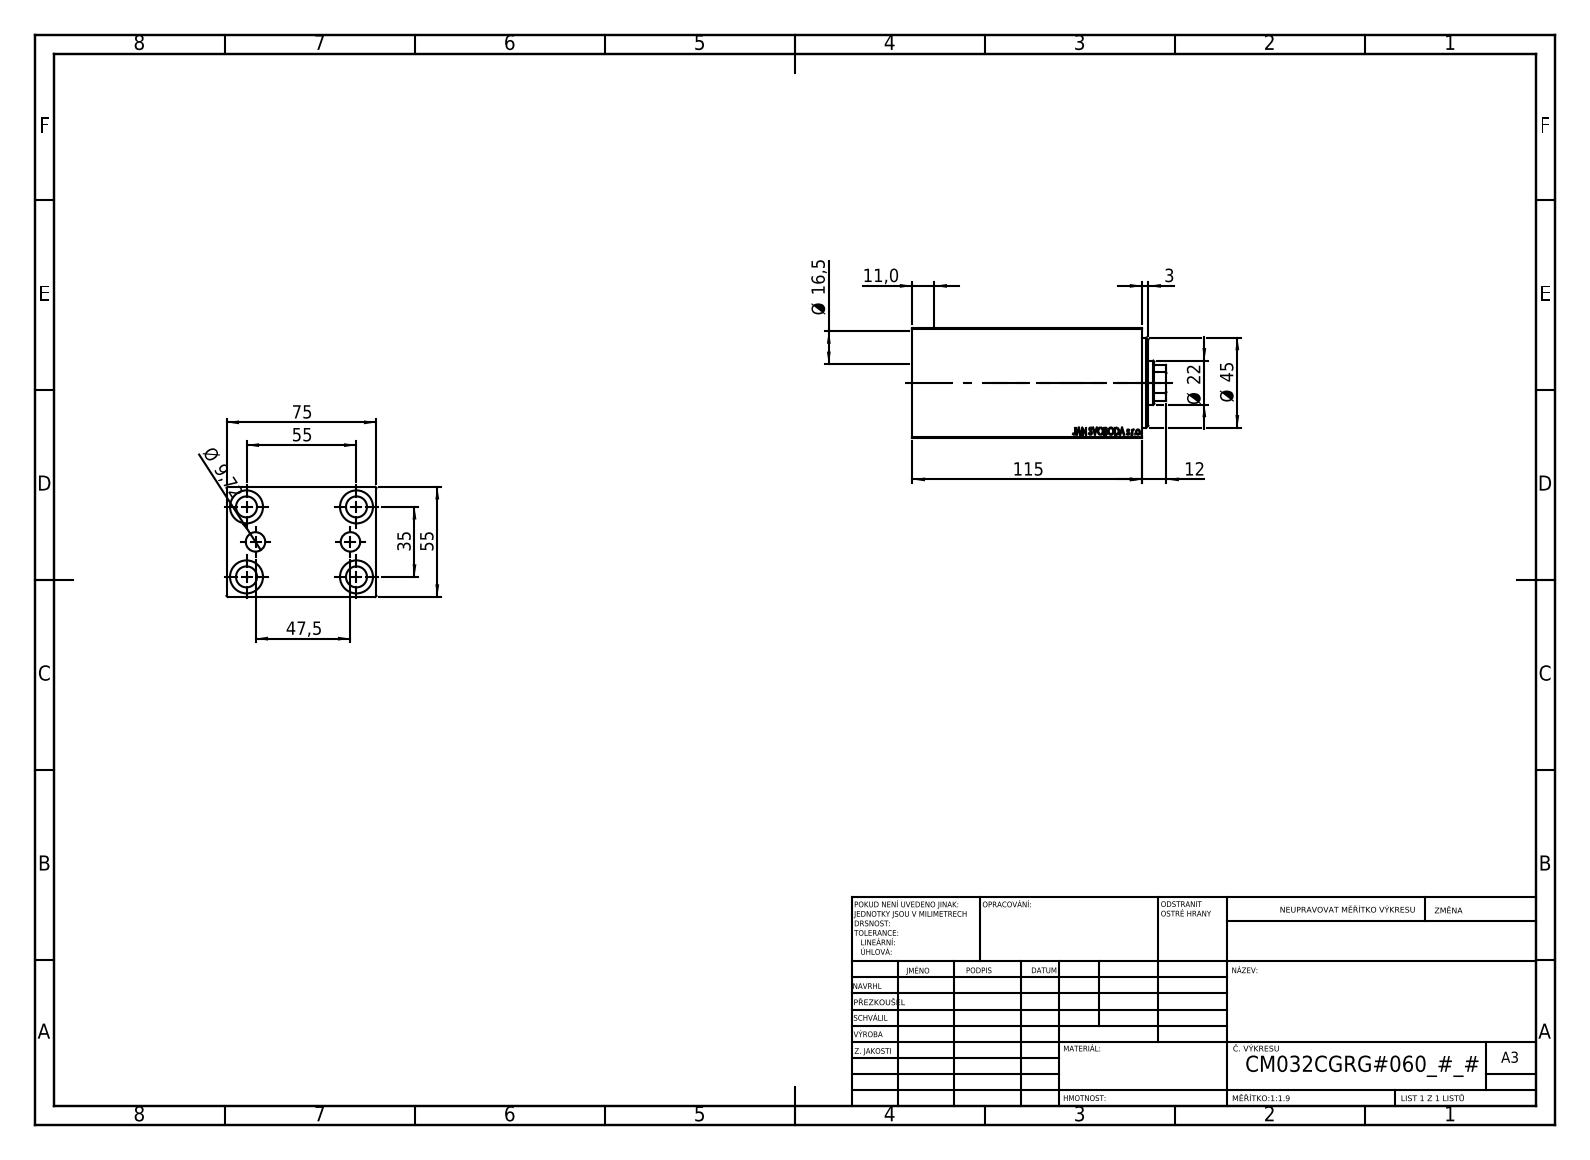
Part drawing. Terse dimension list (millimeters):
name: V450CM_C_Body; V450CM_VC_B; V450CM_C_VCP
written by: SolidWorks 2019 (CONFIG_CONTROL_DESIGN)
unit: mm
bodies: 3 solids, 852 faces (406 planar, 52 cylindrical, 394 other)
size: 127 × 75 × 55
volume: 402 151 mm³; area: 82 151 mm²
holes: 5× ⌀10.5, 4× ⌀16.5, 2× ⌀9.72, 1× ⌀22, 1× ⌀25.5, 1× ⌀32, 1× ⌀34, 1× ⌀45
rounds: 1× R10.5
face distances: 55, 75, 10, 105, 115, 110, 5, 100, 93, 11
hole spacings: 32.6, 17.76, 18.07, 35, 53.45, 54.87, 55, 65.19
